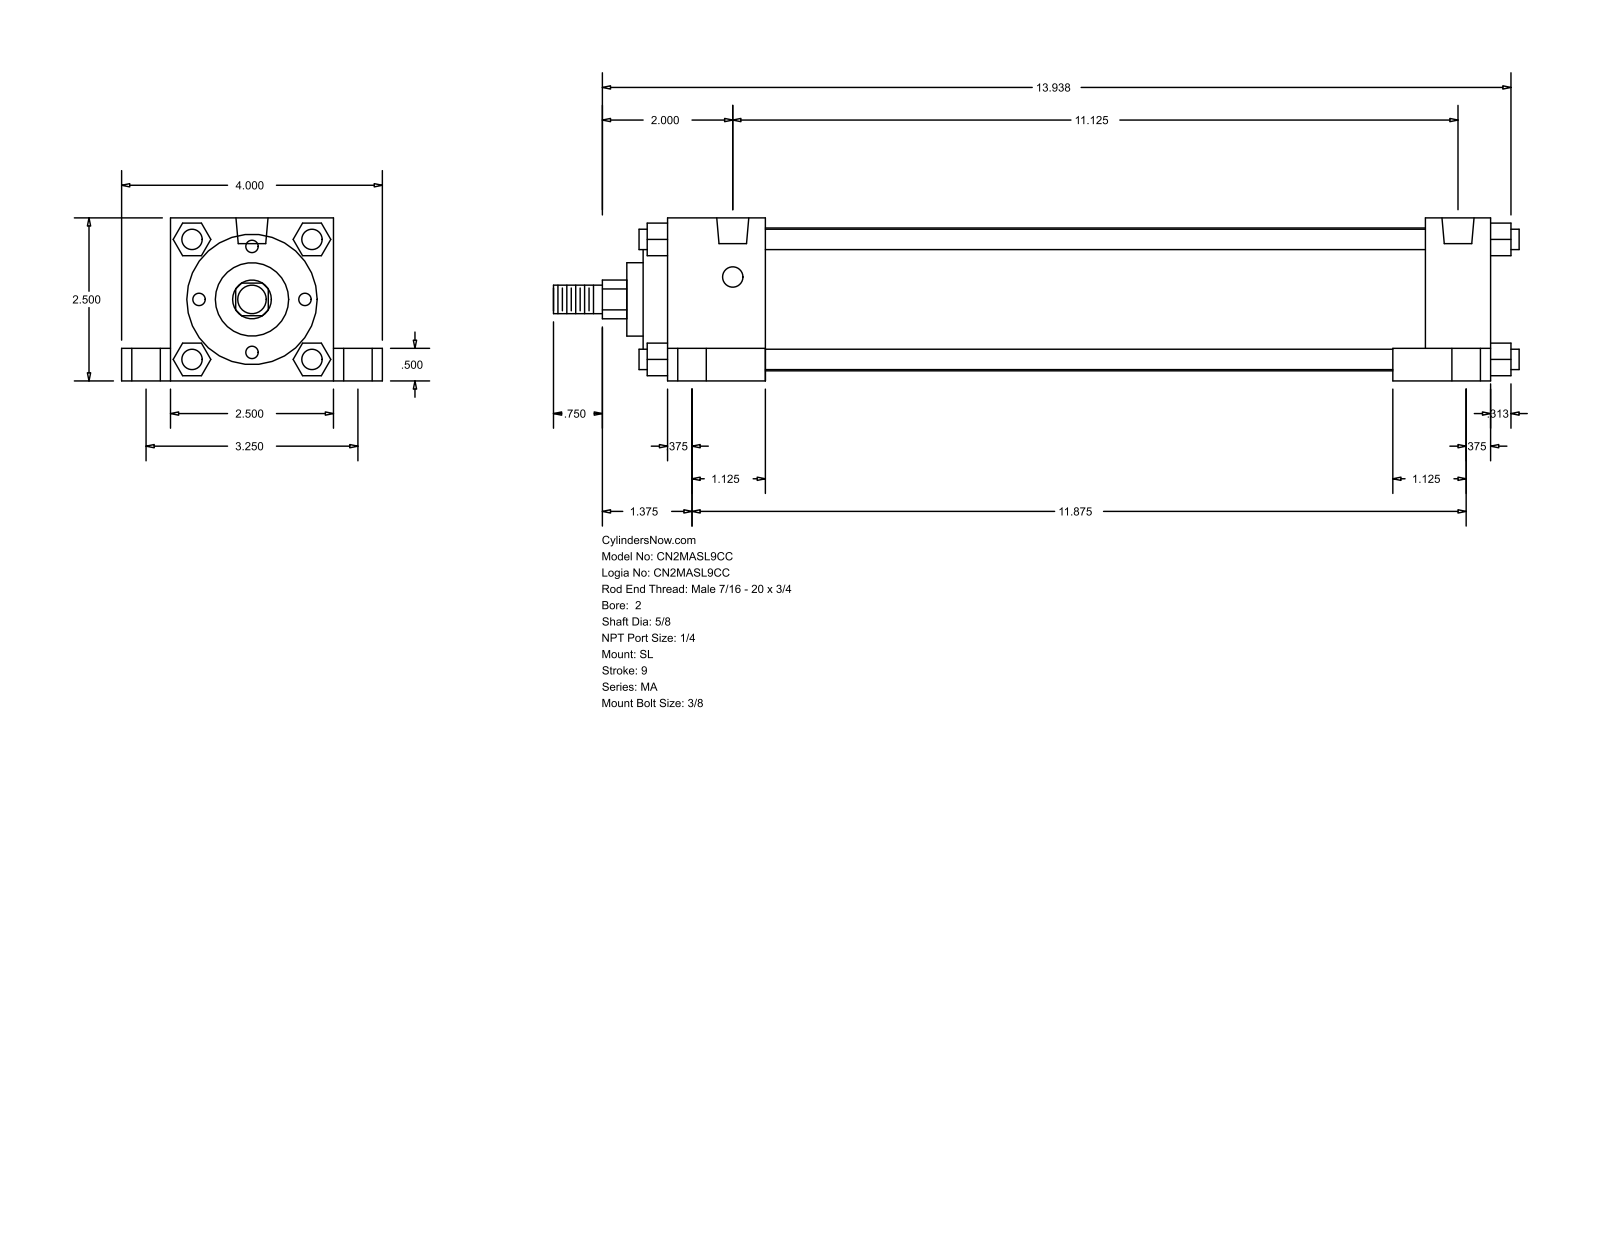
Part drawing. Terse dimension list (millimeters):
name: MA_SL__0200_0.625
written by: GSSL Pune (CONFIG_CONTROL_DESIGN)
unit: mm
bodies: 0 solids, 150 faces (113 planar, 37 cylindrical, 0 other)
size: 376.24 × 101.6 × 63.5
holes: 4× ⌀7.94, 4× ⌀11.11, 4× ⌀17.46, 2× ⌀12.49
bosses: 4× ⌀7.94, 1× ⌀55.63, 1× ⌀50.8, 1× ⌀28.57, 1× ⌀15.88, 1× ⌀11.11
rounds: 1× R7.54
face distances: 63.5, 12.7, 9.52, 19.05, 82.55, 38.1, 50.8, 320.67, 282.57, 295.28
hole spacings: 41.39, 44.22, 82.54, 282.58, 288.71, 301.3, 301.63, 312.72
